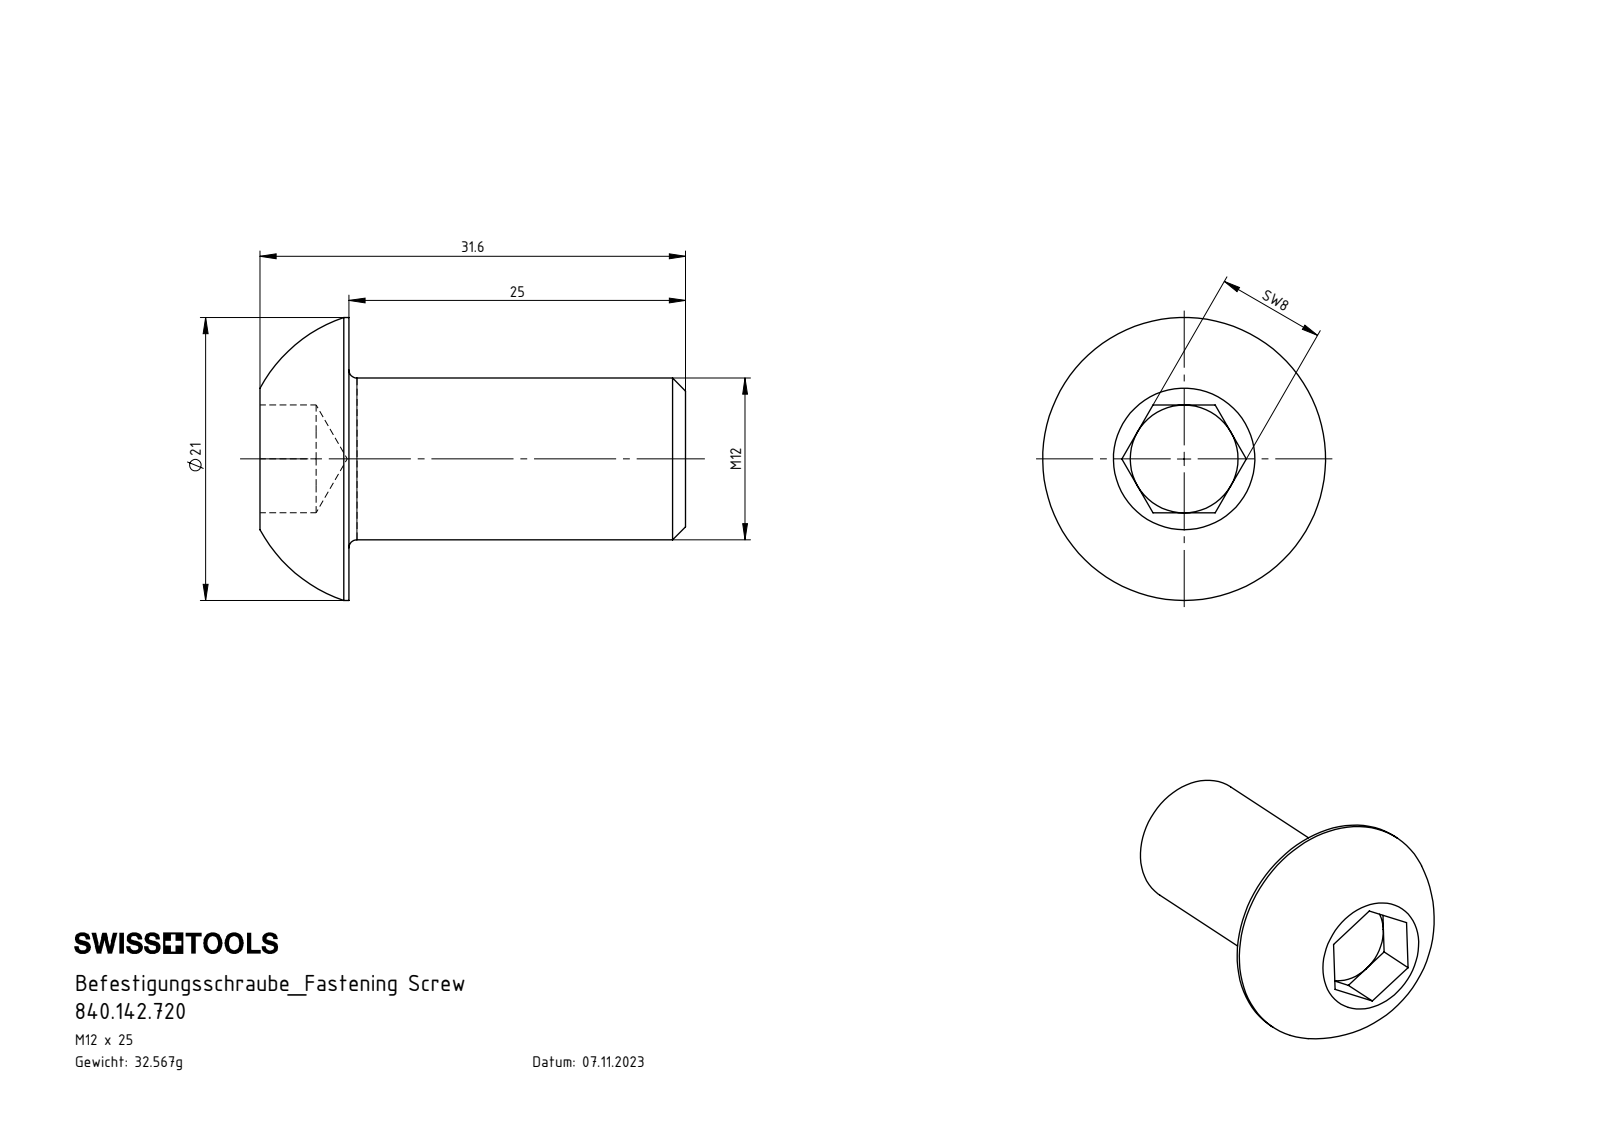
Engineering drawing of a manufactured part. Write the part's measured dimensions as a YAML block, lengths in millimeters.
part_name: "840.142.720"
step_written_by: "SolidWorks 2022 (AUTOMOTIVE_DESIGN)"
units: millimeters
bodies: {solids: 1, faces: 27, planar: 15, cylindrical: 4, other: 8}
overall_size: [31.6, 21, 21]
volume: 4149
surface_area: 1925
round_bosses_or_shafts:
  - {diameter: 21, count: 1}
  - {diameter: 12, count: 1}
face_to_face_distances: [25, 8, 6.6, 31.6, 4.16, 2.44, 27.44]
